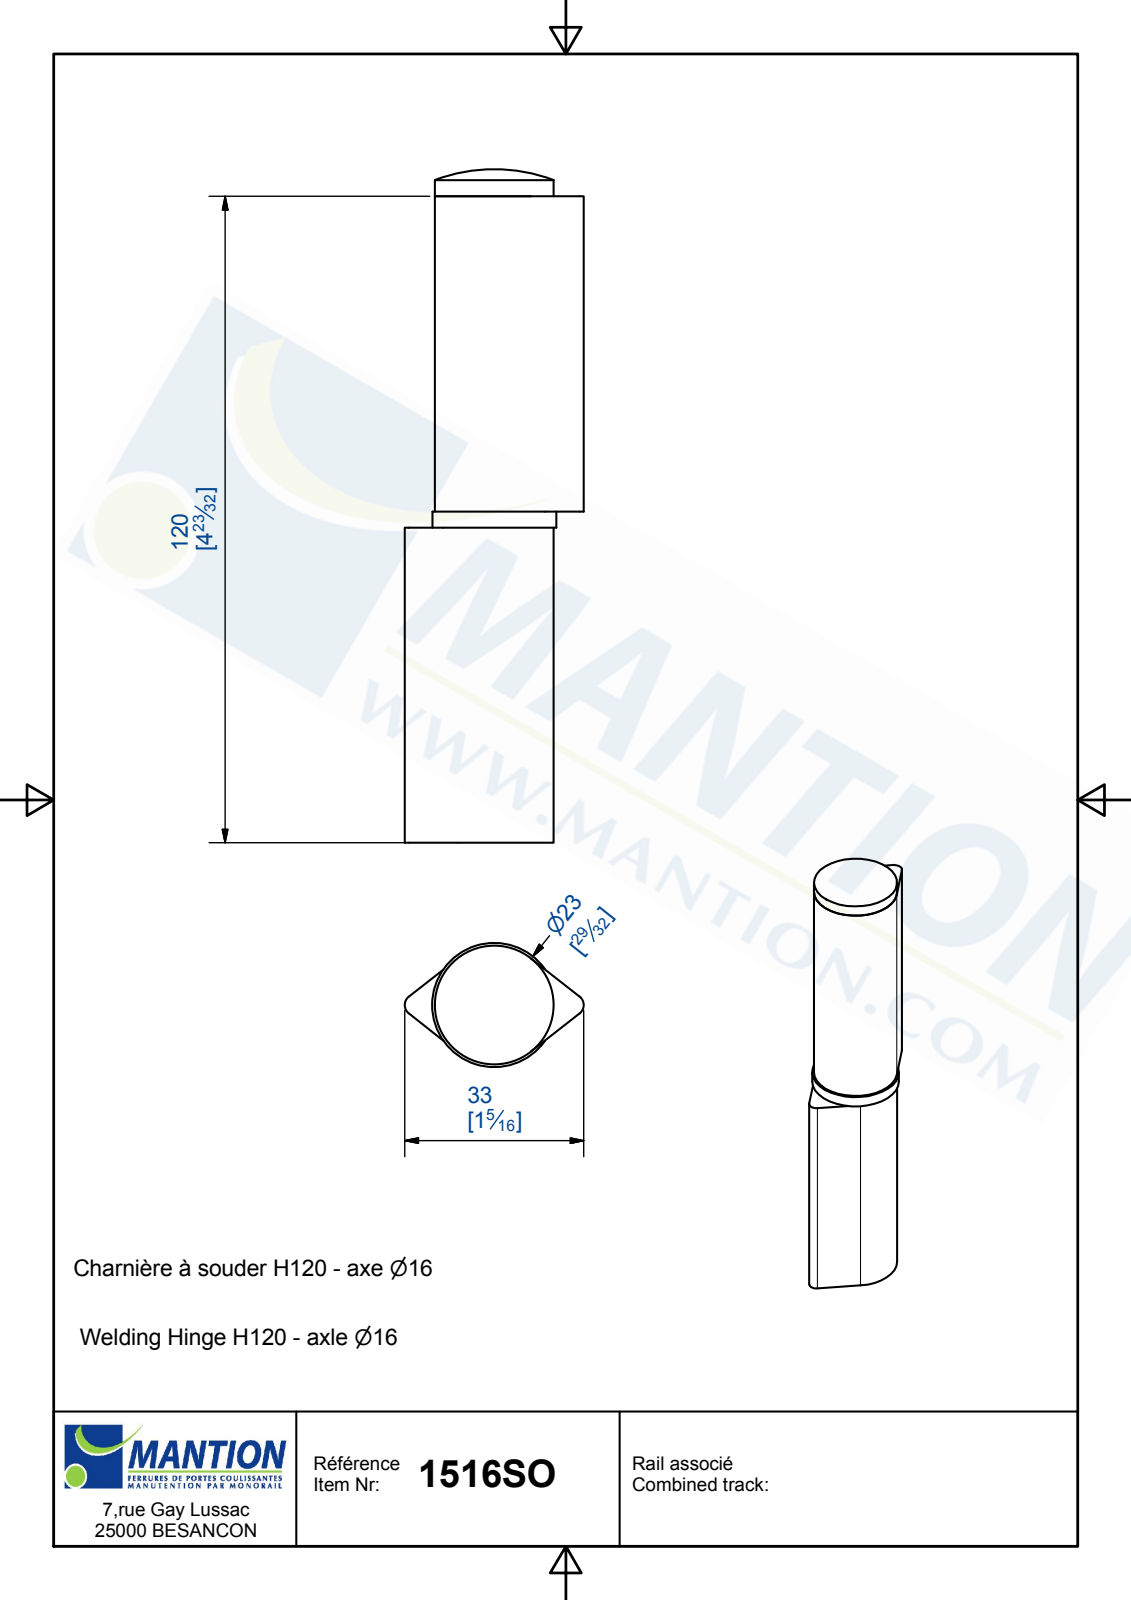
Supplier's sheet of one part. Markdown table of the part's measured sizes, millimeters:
| quantity | value |
| --- | --- |
| part name | 1516SO; 16440; 16511; 15589 |
| STEP written by | Autodesk Inventor 2019 (AUTOMOTIVE_DESIGN) |
| units | millimeters |
| bodies | 4 solids, 173 faces (132 planar, 40 cylindrical, 1 other) |
| overall size | 125 × 35 × 23 |
| volume | 56 786 mm³ |
| surface area | 24 238 mm² |
| round holes (diameter × count) | 16.1 × 1, 16.5 × 1 |
| round bosses / shafts (diameter × count) | 23 × 1, 22 × 1, 16 × 1 |
| partial cylindrical surfaces (radius × count) | 2 × 2, 8.2 × 1 |
| main face-to-face distances | 23, 58.5, 61.5, 3, 120, 118, 59.5, 56.5, 2, 103 |
